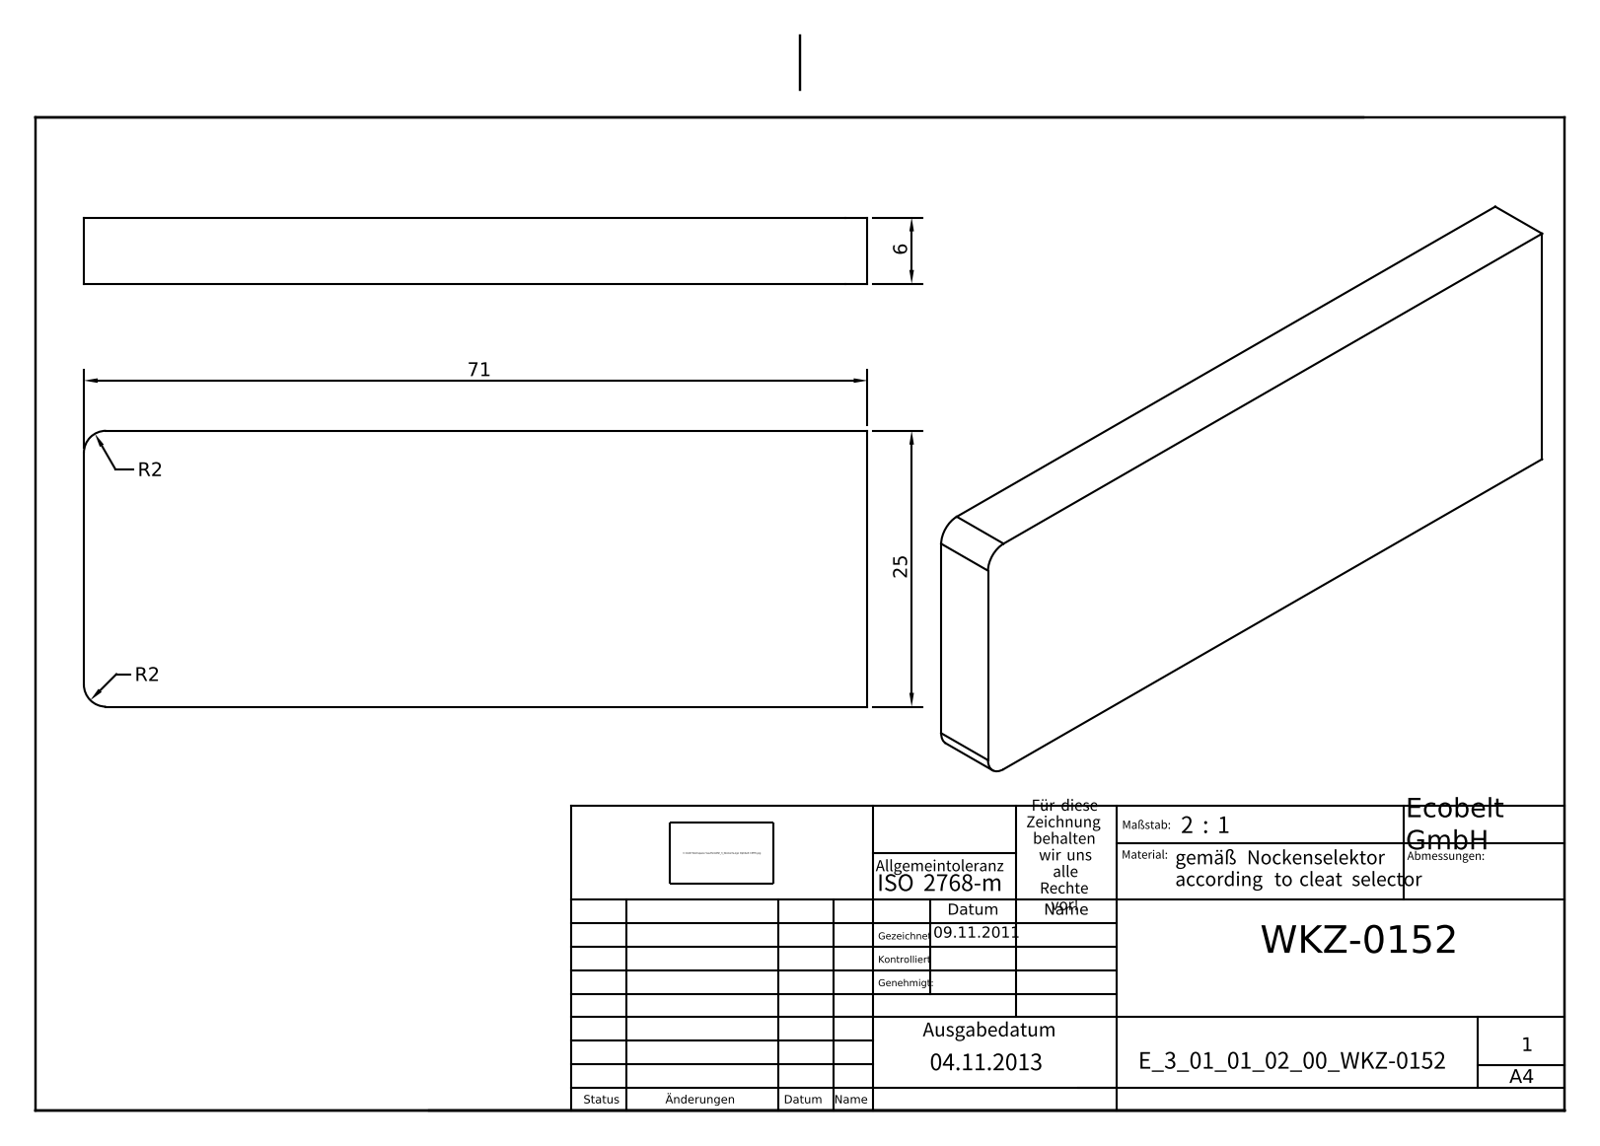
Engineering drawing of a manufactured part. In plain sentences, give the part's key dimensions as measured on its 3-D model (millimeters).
The part is named "E_3_01_01_02_00_WKZ-0152". Its 3-D file was written by "Autodesk Inventor 2021 (AUTOMOTIVE_DESIGN)". It is 1 solid with 8 faces: 6 planar, 2 cylindrical and 0 other. Overall it measures 71 by 25 by 6 millimeters. Its volume is 10 640 cubic millimeters and its surface area 4 688 square millimeters. Partial cylindrical surfaces (rounded edges, fillets, slot ends): 2 of radius 2. The main face-to-face distances are 6, 25, 71.
